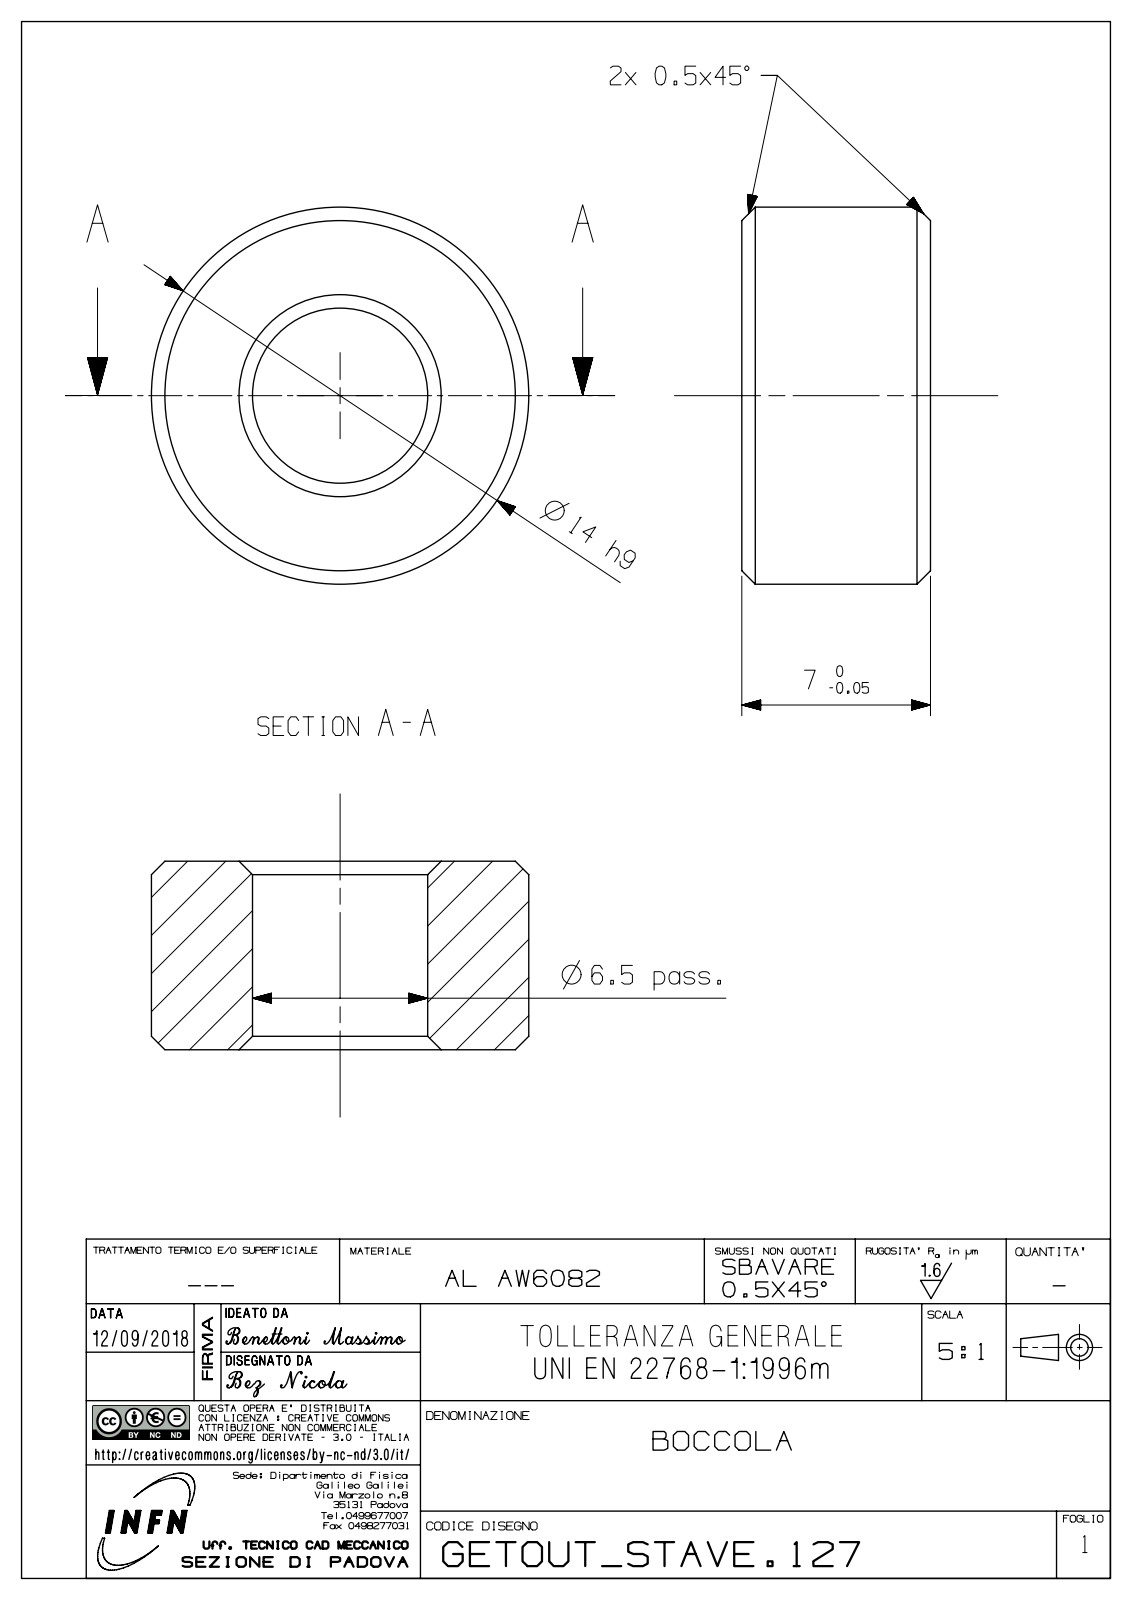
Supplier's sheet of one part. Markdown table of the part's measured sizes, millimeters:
| quantity | value |
| --- | --- |
| part name | bezA730AE56cd3v |
| STEP written by | SIEMENS PLM Software NX 12.0 (AUTOMOTIVE_DESIGN) |
| units | millimeters |
| bodies | 1 solid, 8 faces (2 planar, 2 cylindrical, 4 other) |
| overall size | 14 × 14 × 7 |
| volume | 829 mm³ |
| surface area | 655 mm² |
| round holes (diameter × count) | 6.5 × 1 |
| round bosses / shafts (diameter × count) | 14 × 1 |
| main face-to-face distances | 7 |
